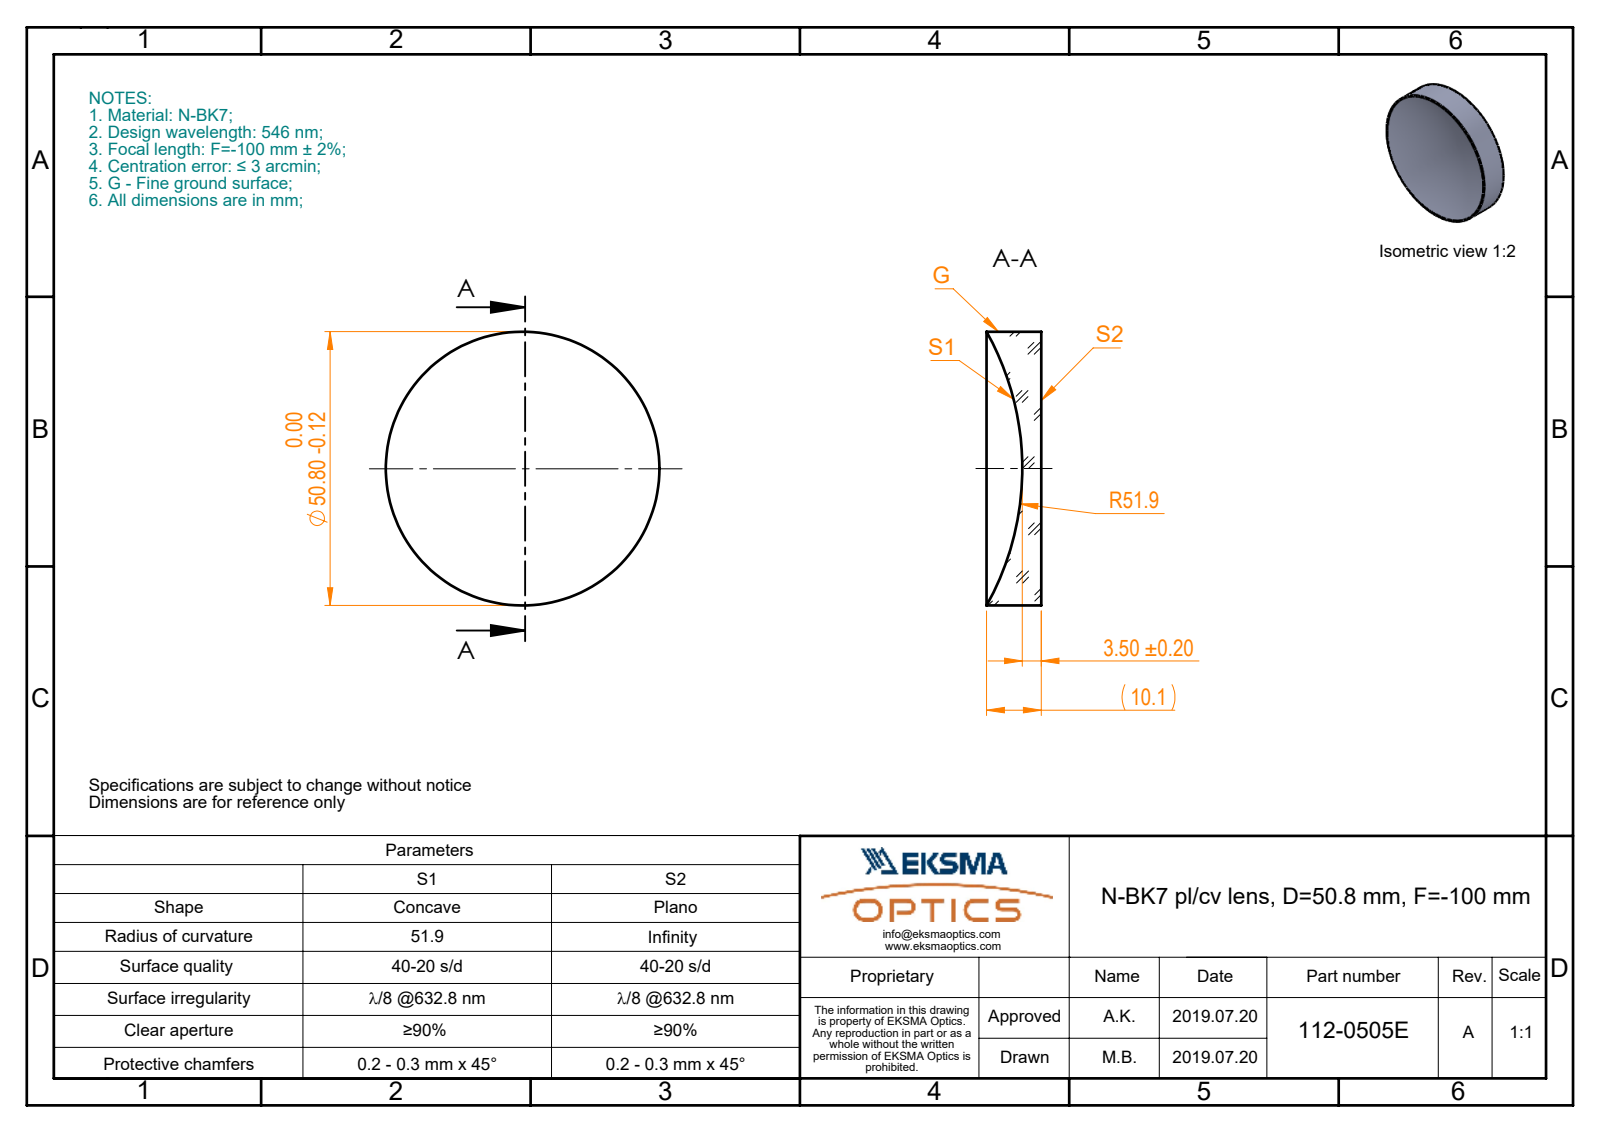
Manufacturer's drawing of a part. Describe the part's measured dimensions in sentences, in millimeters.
The part is named "112-0505 BK7 pl-cv 50.8 F-100". Its 3-D file was written by "SolidWorks 2017 (CONFIG_CONTROL_DESIGN)". It is 1 solid with 5 faces: 1 planar, 2 cylindrical and 2 other. Overall it measures 50.8 by 50.8 by 10.14 millimeters. Its volume is 13 674 cubic millimeters and its surface area 5 811 square millimeters. Round bosses or shafts: 1 of diameter 50.8.
